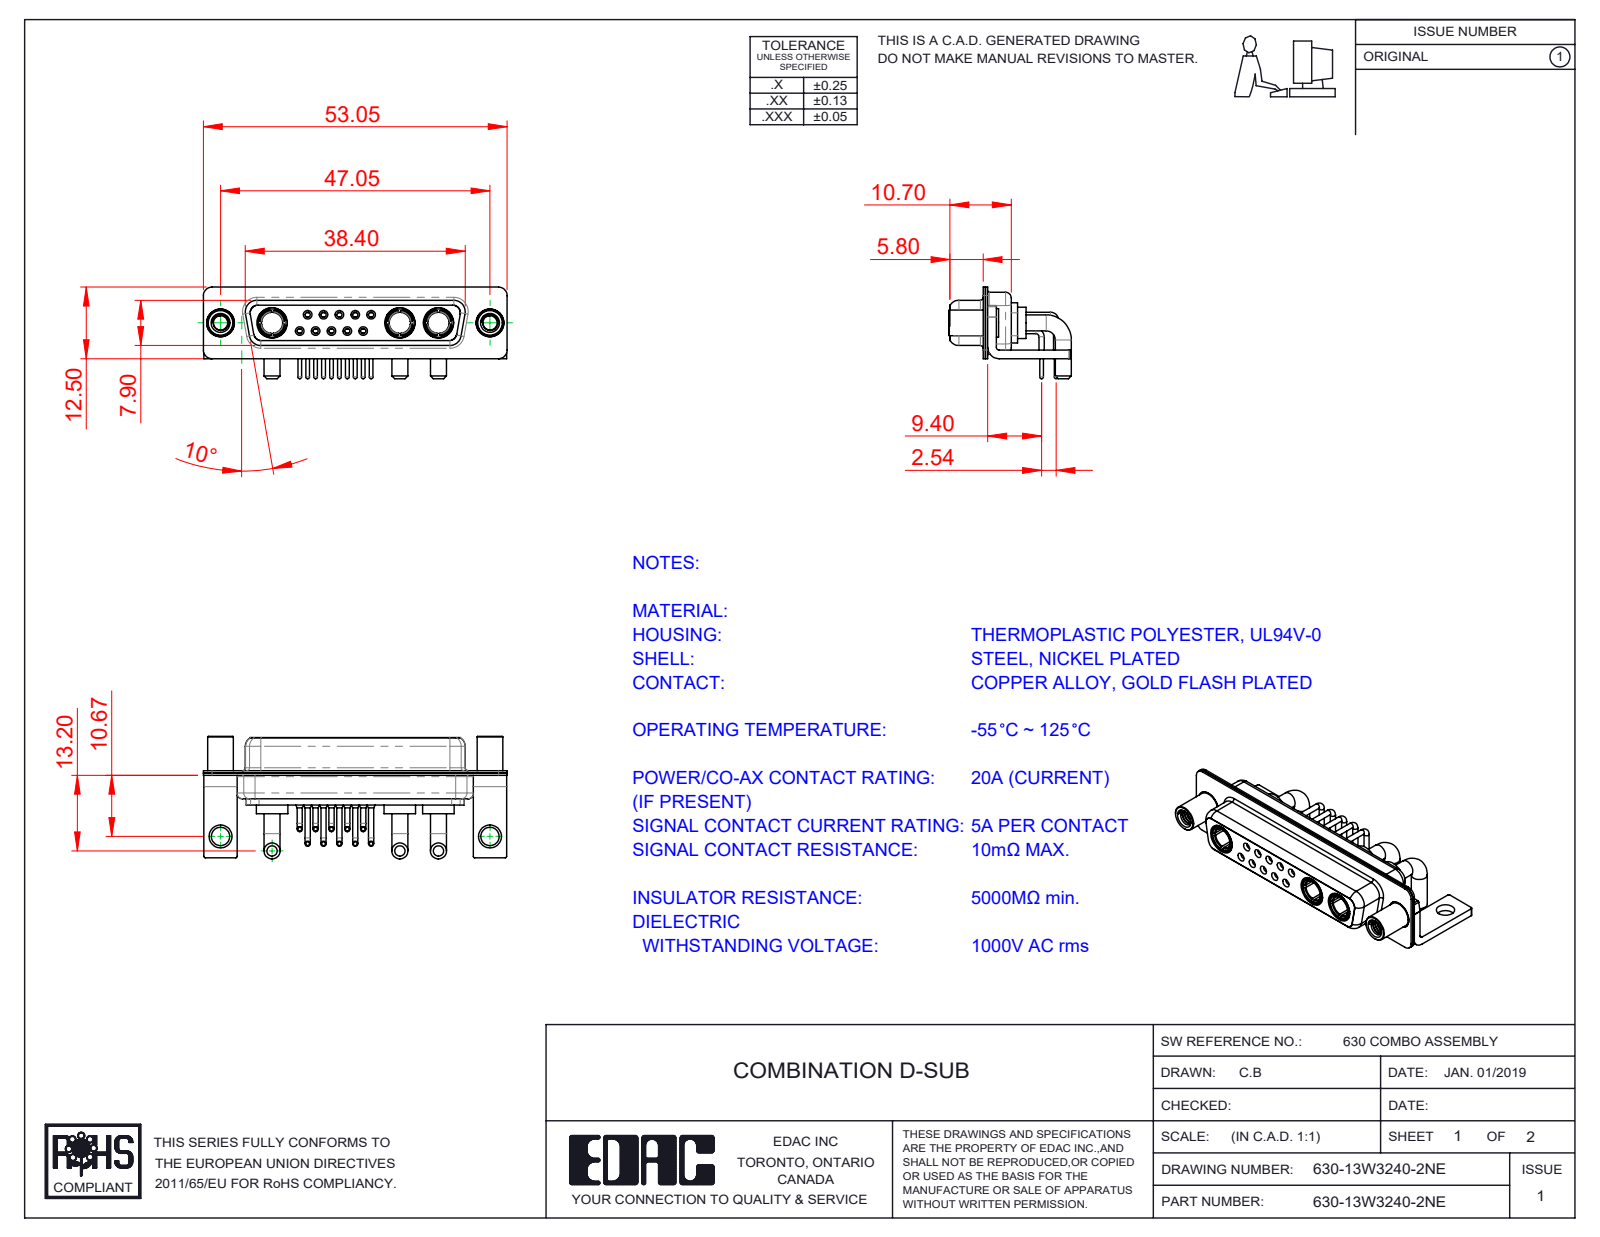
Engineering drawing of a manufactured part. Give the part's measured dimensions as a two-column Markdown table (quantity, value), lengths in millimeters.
| quantity | value |
| --- | --- |
| part name | 630Combo Contact Row 1; 630Combo Stabilizer Bracket; 630Combo Shell Rear_25 Contacts; 630Combo Contact Row 2 (+5 more) |
| STEP written by | SolidWorks 2020 (CONFIG_CONTROL_DESIGN) |
| units | millimeters |
| bodies | 23 solids, 1141 faces (326 planar, 514 cylindrical, 301 other) |
| overall size | 53.05 × 21.4 × 16 |
| volume | 4 409 mm³ |
| surface area | 9 943 mm² |
| round holes (diameter × count) | 0.9 × 10, 1.1 × 10, 1.5 × 10, 2 × 10, 1.6 × 5, 1.7 × 5, 4.85 × 5, 3.7 × 3, 5.3 × 3, 2.5 × 2, 3.2 × 2, 4 × 2 |
| round bosses / shafts (diameter × count) | 0.9 × 10, 0.65 × 10, 2.8 × 6, 1.6 × 5, 5.5 × 3, 5.2 × 3, 4.96 × 3, 4.75 × 3 |
| partial cylindrical surfaces (radius × count) | 0.25 × 16, 1.5 × 16, 2 × 13, 1.35 × 8, 1.6 × 8, 0.5 × 5, 0.6 × 4, 0.65 × 4 |
| main face-to-face distances | 0.4, 0.45, 1.4, 8.45, 1.8, 8.9, 0.8, 6.2, 1.5, 7.05 |
| hole center spacings | 3.16, 2.77, 5.54, 5.03, 5.04, 8.31, 7.48, 7.49 |
